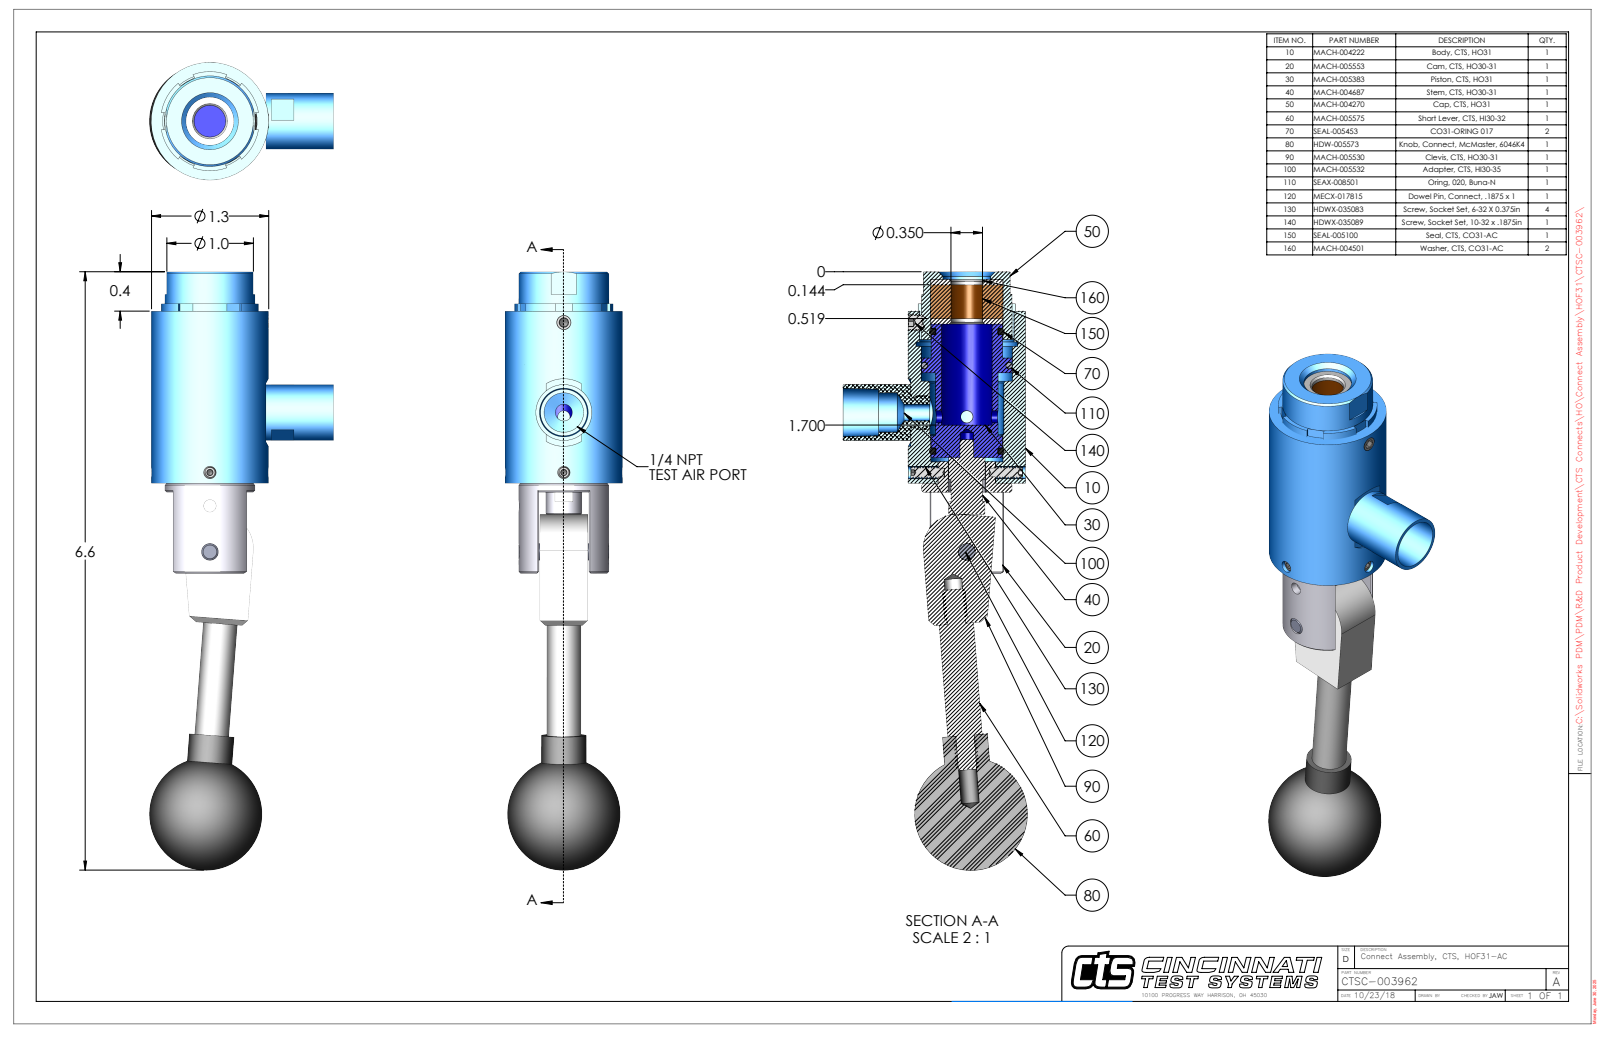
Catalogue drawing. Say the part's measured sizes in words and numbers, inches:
The part is named "CTSC-003962". Its 3-D file was written by "SolidWorks 2023 (AUTOMOTIVE_DESIGN)". It is 14 solids with 532 faces: 173 planar, 217 cylindrical and 142 other. Overall it measures 6.636 by 2.042 by 1.3 inches. Its volume is 4.53 cubic inches and its surface area 46.71 square inches. Round holes: 2 of diameter 0.136, 2 of diameter 0.201, 1 of diameter 0.138, 1 of diameter 0.15, 1 of diameter 0.159, 1 of diameter 0.187, 1 of diameter 0.189, 1 of diameter 0.19, 1 of diameter 0.332, 1 of diameter 0.35, 1 of diameter 0.352, 1 of diameter 0.418. Round bosses or shafts: 2 of diameter 0.138, 1 of diameter 1.3, 1 of diameter 1, 1 of diameter 0.792, 1 of diameter 0.79, 1 of diameter 0.69, 1 of diameter 0.63, 1 of diameter 0.62. Partial cylindrical surfaces (rounded edges, fillets, slot ends): 1 of radius 0.374, 1 of radius 0.375, 1 of radius 0.524, 1 of radius 0.547. The main face-to-face distances are 0.012, 0.542, 0.434, 0.059, 0.375, 0.53, 0.554, 1.825, 2.2, 2.259. The hole center spacings are 0.047, 0.51, 0.987, 0.997, 1.044, 1.497.
